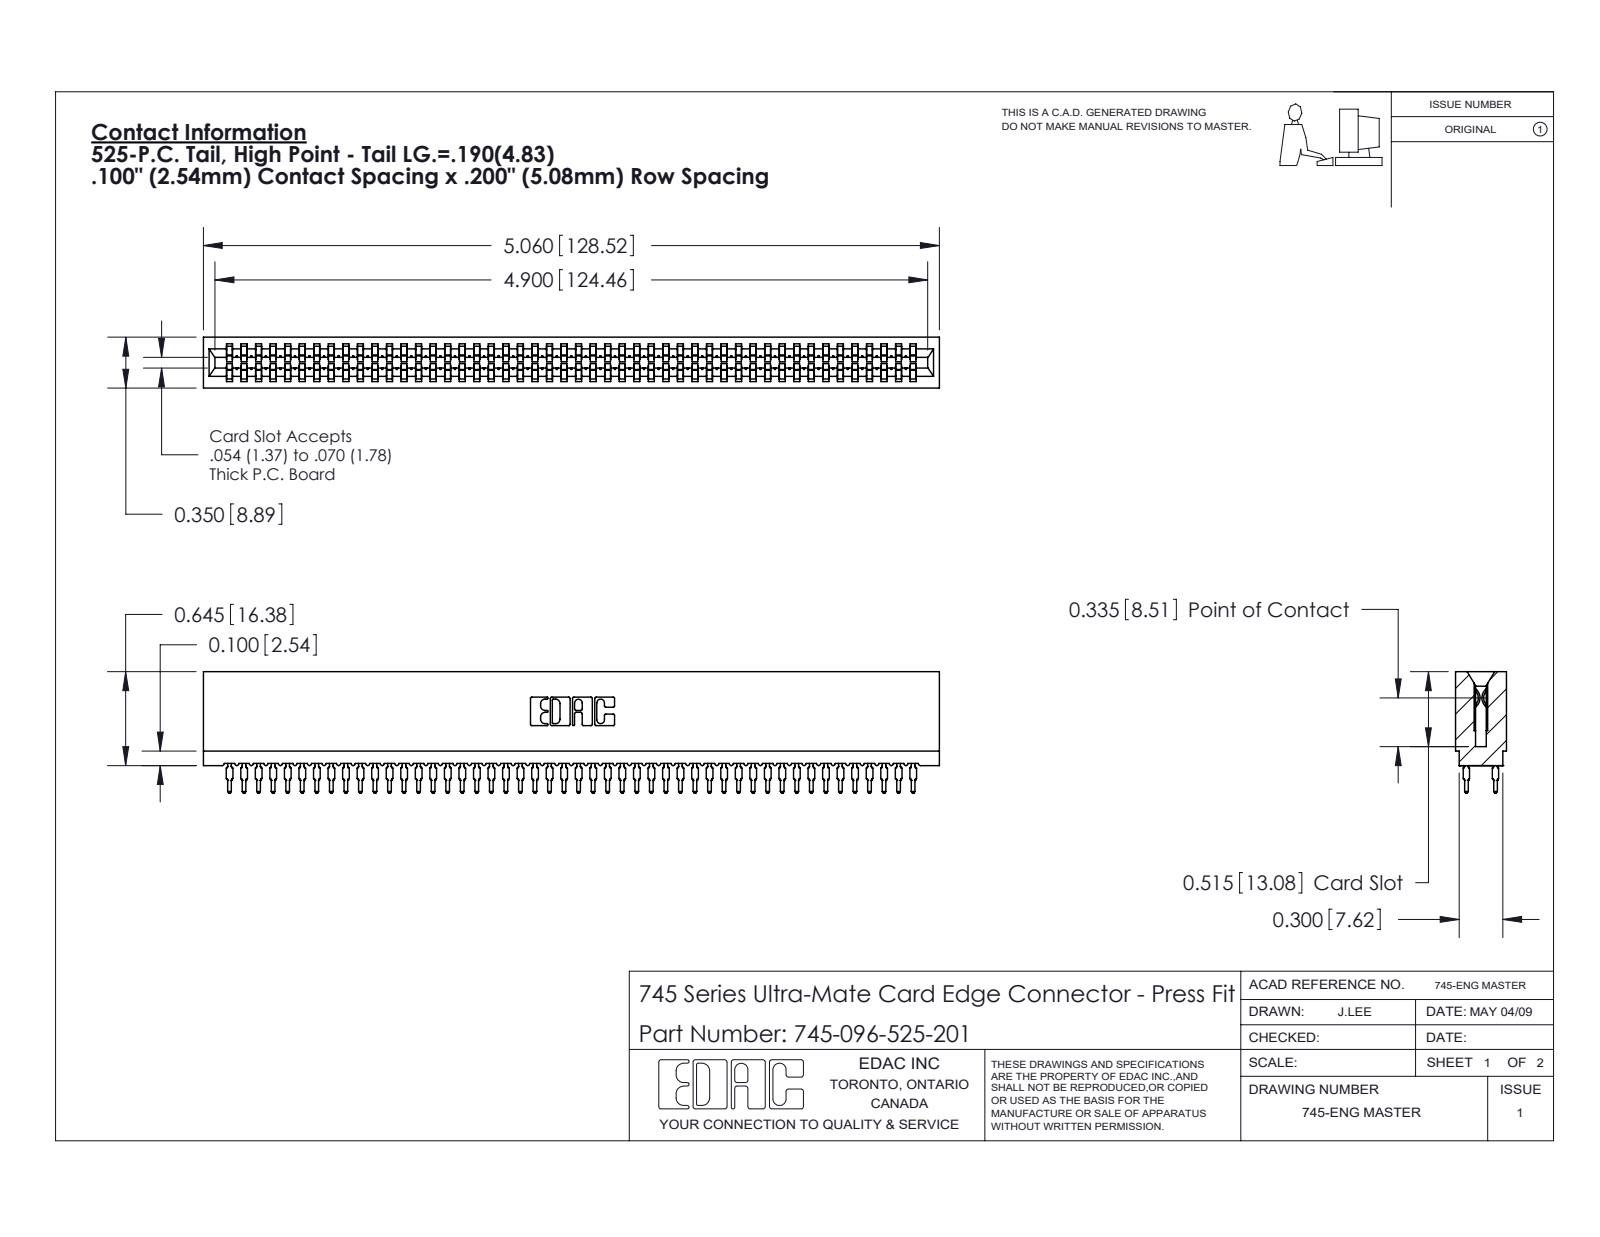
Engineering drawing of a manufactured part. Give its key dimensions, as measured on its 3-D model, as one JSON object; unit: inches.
{"part_name": "745-096-525-201; 745-292-001_525; 745 Part_Insulator Option - 01", "step_written_by": "SolidWorks 2020 (CONFIG_CONTROL_DESIGN)", "units": "inches", "bodies": {"solids": 97, "faces": 8687, "planar": 4471, "cylindrical": 1720, "other": 2496}, "overall_size": [5.06, 0.836, 0.35], "volume_in3": 0.703, "surface_area_in2": 36.35, "partial_cylinders_radius": [[0.021, 192], [0.015, 96], [0.01, 22], [0.005, 8], [0.011, 8], [0.007, 6], [0.031, 6], [0.026, 3]], "face_to_face_distances": [0.35, 0.063, 0.287, 0.045, 0.305, 0.018, 0.243, 0.138, 0.212, 0.093]}
